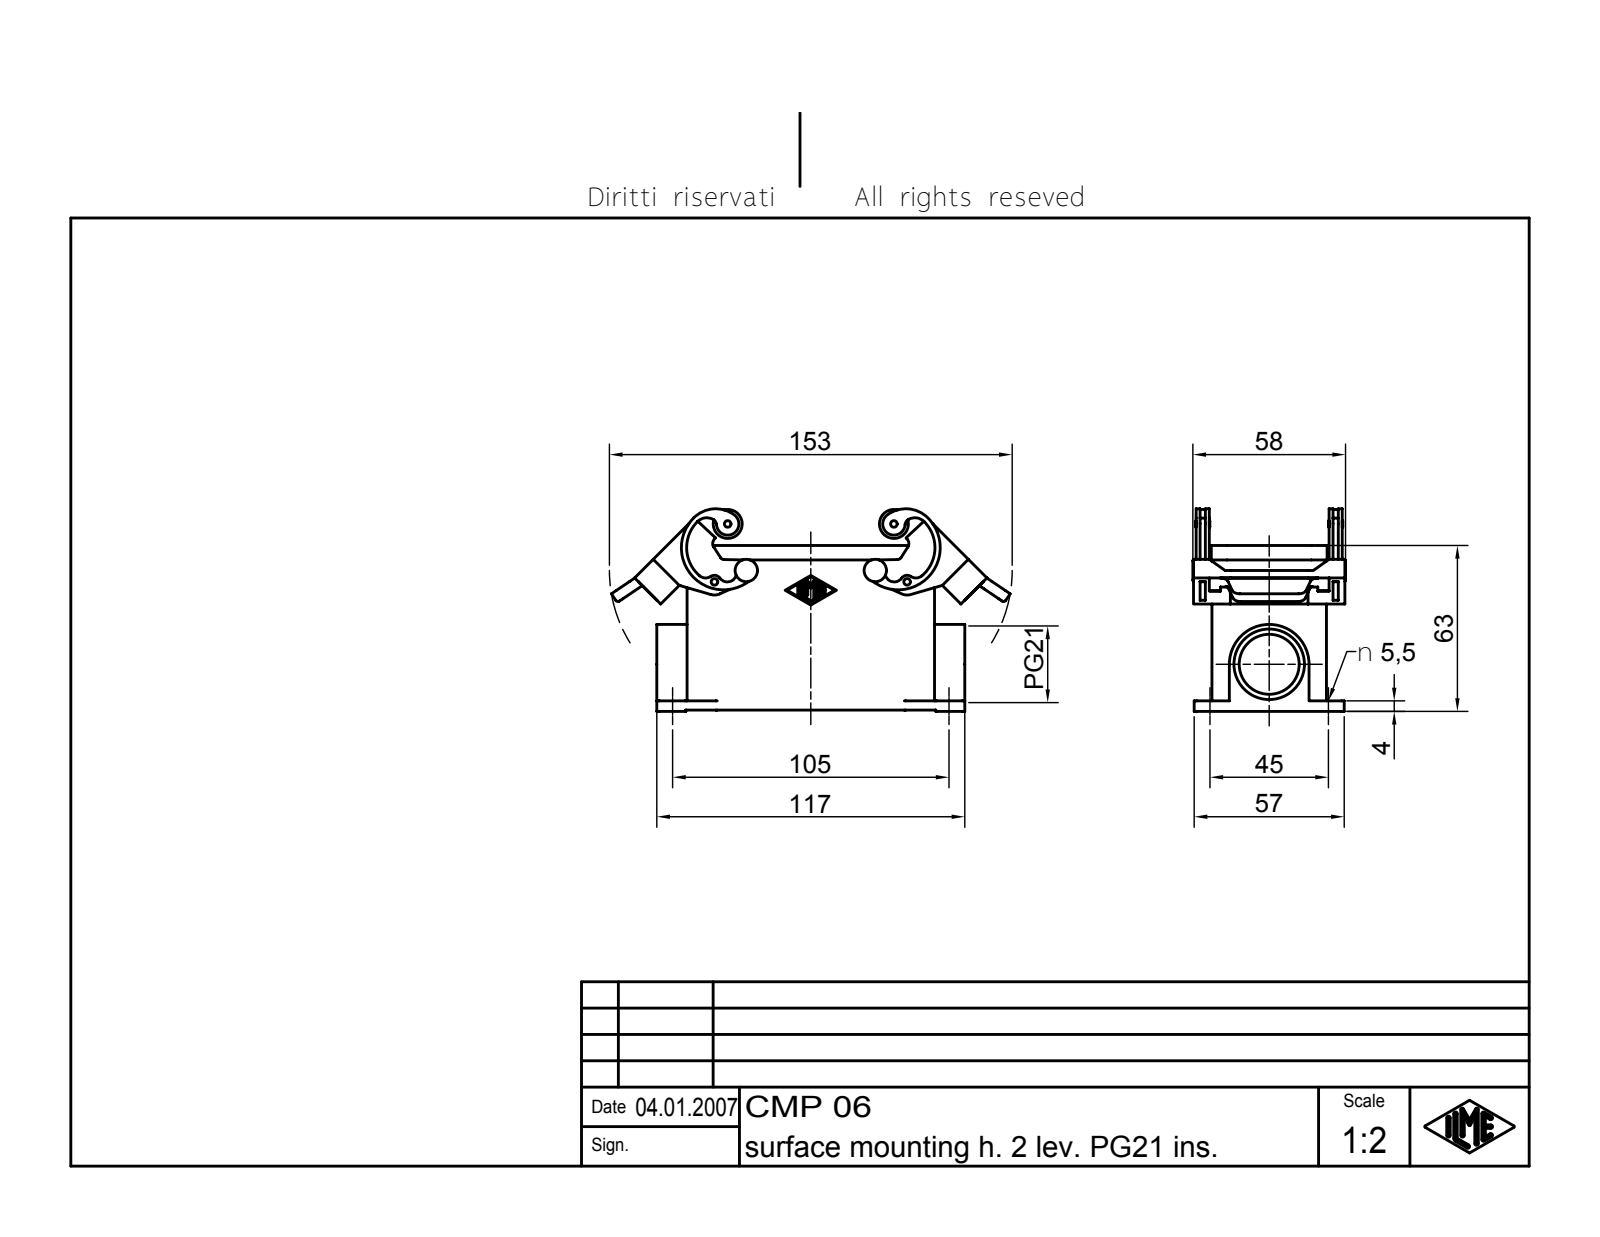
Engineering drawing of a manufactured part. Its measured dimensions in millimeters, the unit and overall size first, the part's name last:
Units: millimetres
Overall size (bounding box): 151.49 × 76.94 × 58
Round holes (diameter × count): ⌀2 ×4, ⌀5.5 ×4, ⌀2.5 ×2, ⌀22.78 ×1, ⌀26.78 ×1
Round bosses / shafts (diameter × count): ⌀11 ×2, ⌀5 ×2, ⌀3 ×2
Partial cylindrical surfaces — rounded edges, fillets, slot ends (radius × count): R1 ×20, R0.38 ×14, R3 ×12, R6 ×8, R2.5 ×6, R1.5 ×4, R2 ×4, R3.5 ×4
Main face-to-face distances: 3, 40.5, 43.5, 3.5, 37.5, 4, 50.5, 0.75, 40.75, 4.5
Hole centre spacings: 22.56, 45, 71.62, 105, 114.24, 63.14, 73.18
Volume: 106 794 mm³ · Surface area: 62 172 mm²
Bodies: 1 solid, 749 faces (191 planar, 205 cylindrical, 353 other)
Part name (STEP PRODUCT): CMP 06
STEP written by: Autodesk Inventor 7 (AUTOMOTIVE_DESIGN)
